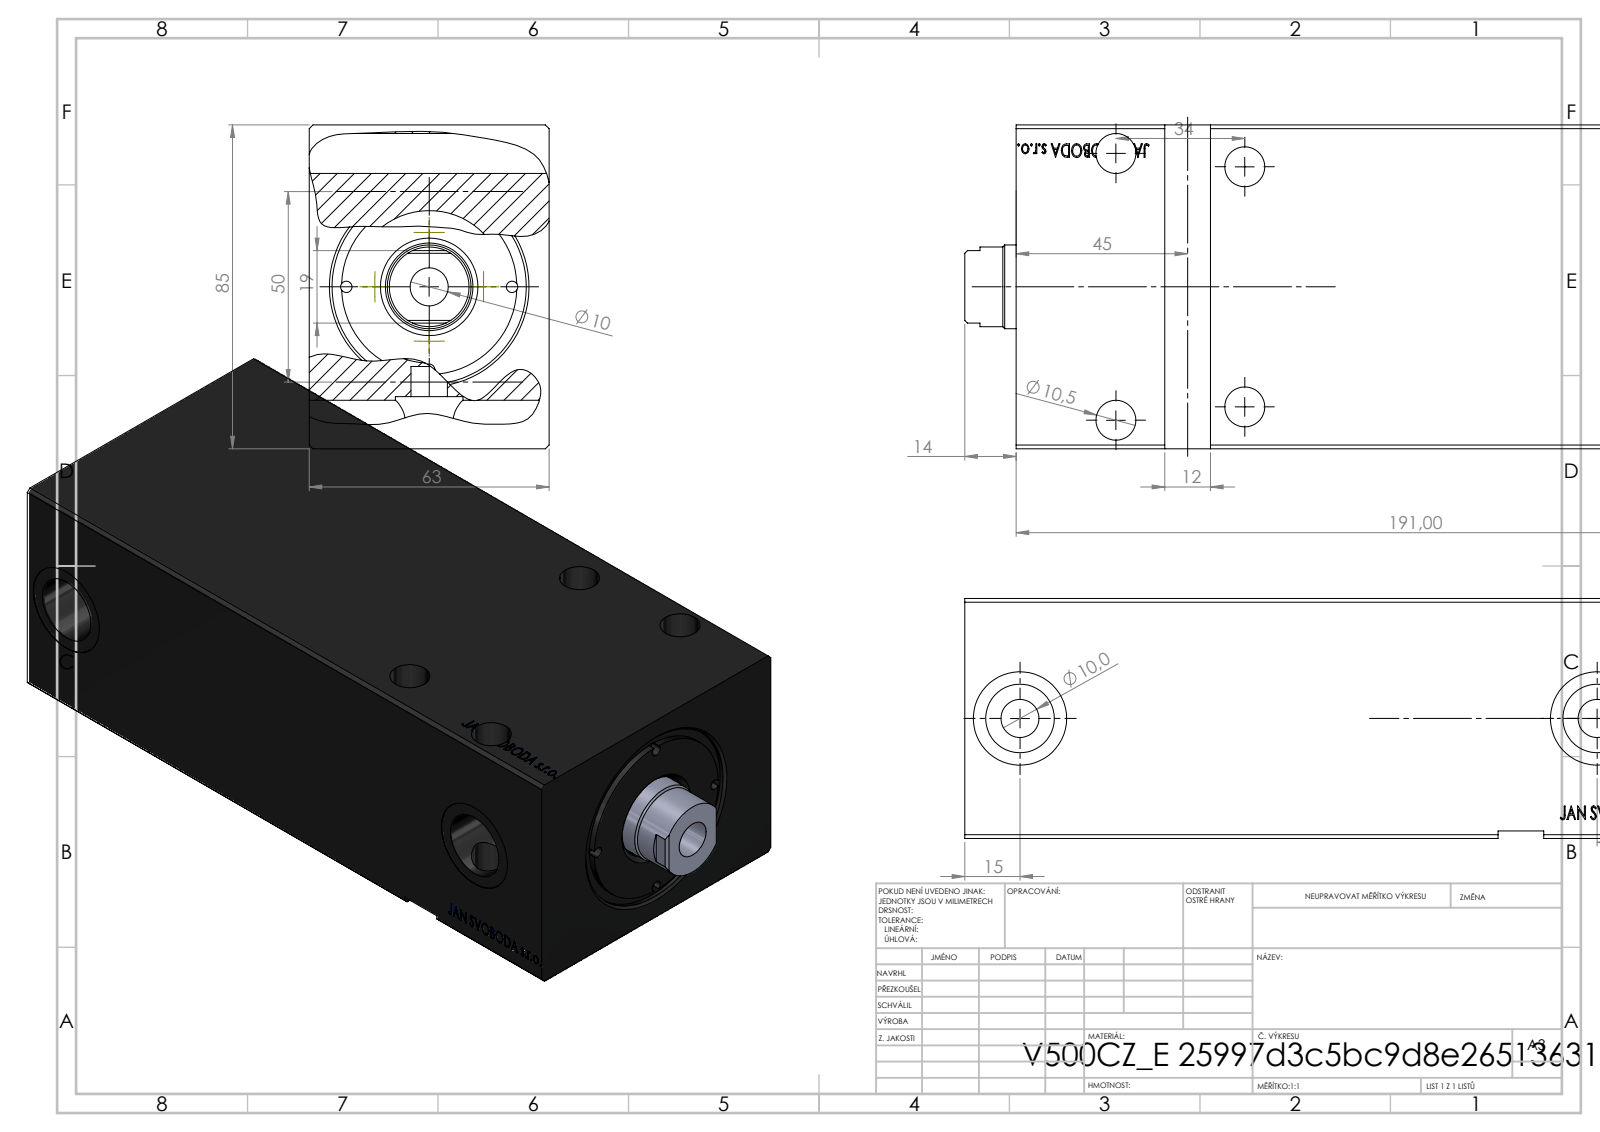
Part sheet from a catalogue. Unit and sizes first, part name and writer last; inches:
Units: inches
Overall size (bounding box): 8.051 × 3.346 × 2.48
Round holes (diameter × count): ⌀0.118 ×4, ⌀0.413 ×4, ⌀0.394 ×3, ⌀0.709 ×2, ⌀0.965 ×2, ⌀0.866 ×1, ⌀0.906 ×1, ⌀1.417 ×1, ⌀1.575 ×1, ⌀2.008 ×1
Round bosses / shafts (diameter × count): ⌀1.811 ×1, ⌀0.824 ×1
Main face-to-face distances: 2.48, 3.346, 7.52, 6.102, 1.417, 2.402, 0.465, 5.638, 7.055, 0.071
Hole centre spacings: 0.856, 1.211, 1.339, 1.713, 2.937, 2.48, 2.756, 5.965
Volume: 54.4 in³ · Surface area: 183.2 in²
Bodies: 3 solids, 779 faces (365 planar, 54 cylindrical, 360 other)
Part name (STEP PRODUCT): V500CZ_VC_vysunovaci_E; V500CZ_E; V500CZ_VCP_E
STEP written by: SolidWorks 2019 (CONFIG_CONTROL_DESIGN)
